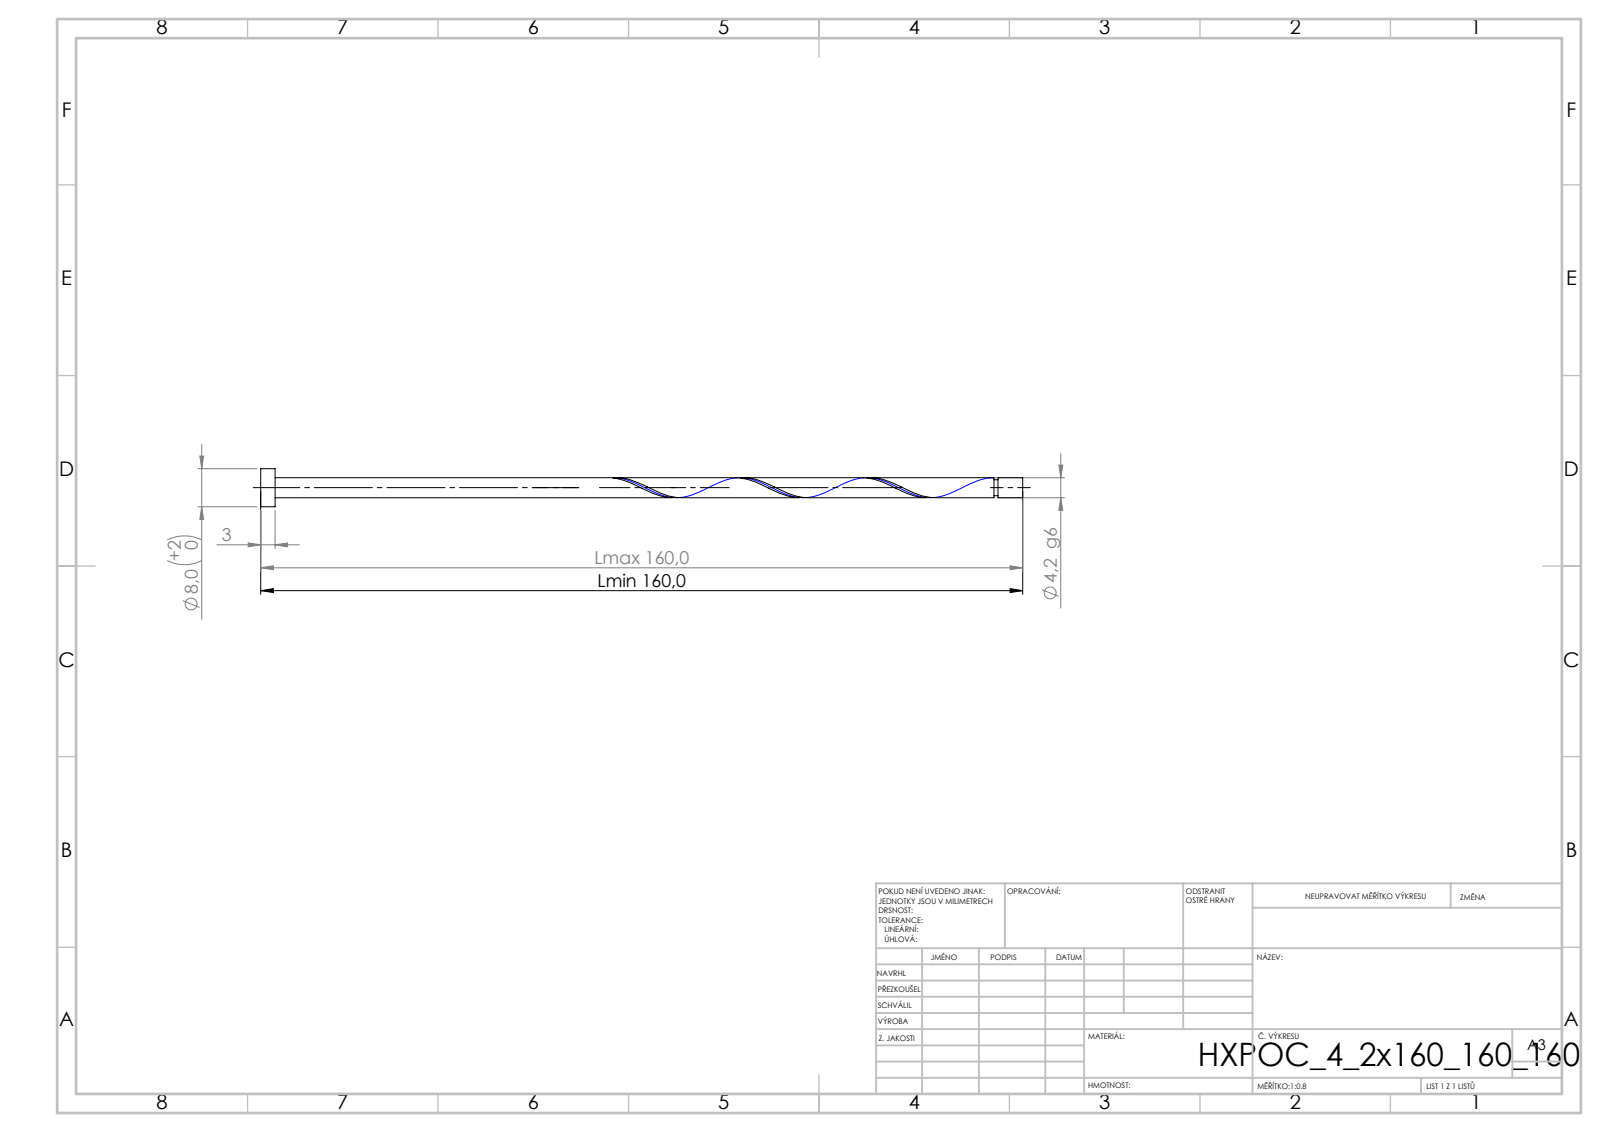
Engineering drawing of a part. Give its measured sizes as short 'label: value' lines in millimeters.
written by: SolidWorks 2019 (CONFIG_CONTROL_DESIGN)
unit: mm
bodies: 1 solid, 21 faces (6 planar, 14 cylindrical, 1 other)
size: 160 × 8 × 8
volume: 2 301 mm³; area: 2 292 mm²
bosses: 1× ⌀8, 1× ⌀4.2, 1× ⌀3.36
face distances: 3, 160, 157, 154.81, 151.81, 5.19, 153.97, 150.97, 0.84, 6.03
